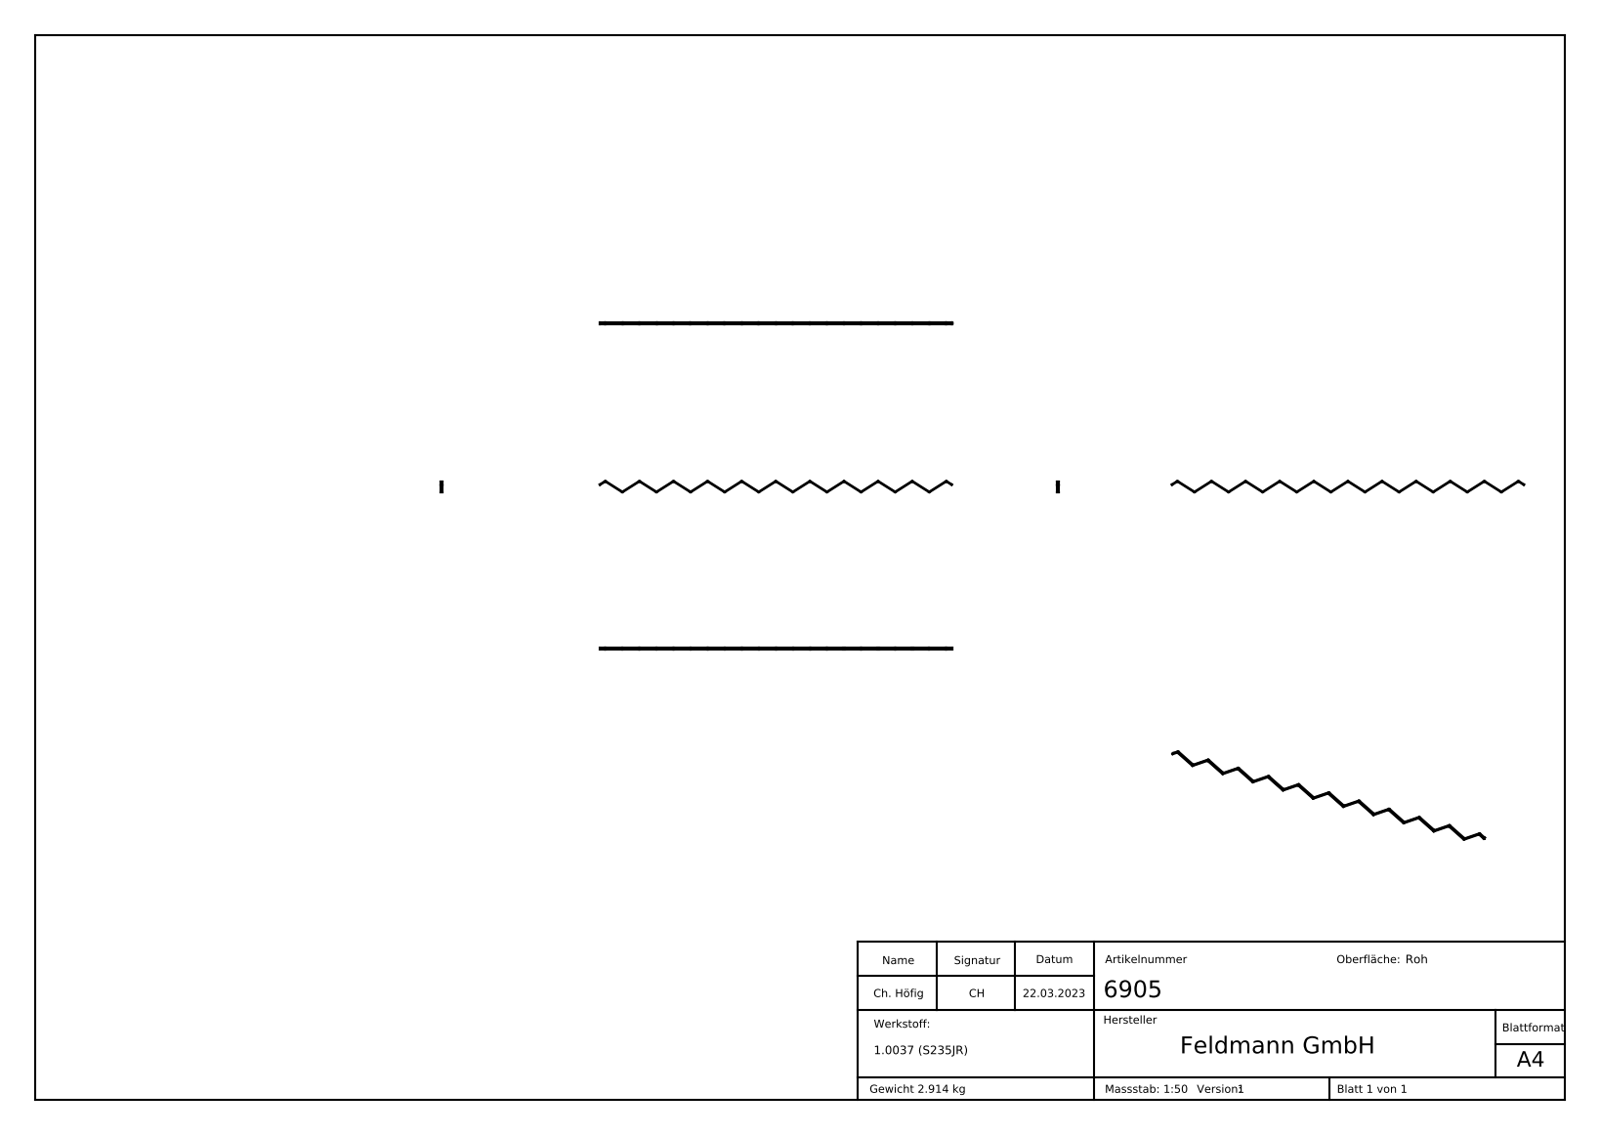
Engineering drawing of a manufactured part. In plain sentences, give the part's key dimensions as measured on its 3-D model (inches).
The part is named "6905". Its 3-D file was written by "SolidWorks 2018 (CONFIG_CONTROL_DESIGN)". It is 1 solid with 384 faces: 239 planar, 42 cylindrical and 103 other. Overall it measures 130.174 by 4.134 by 0.63 inches. Its volume is 22.8 cubic inches and its surface area 265.7 square inches. Partial cylindrical surfaces (rounded edges, fillets, slot ends): 11 of radius 0.197, 11 of radius 0.433, 10 of radius 0.079, 10 of radius 0.315. The main face-to-face distances are 6.74, 13.48, 20.22, 26.961, 0.236, 33.701, 6.976, 6.504, 13.717, 13.244.
